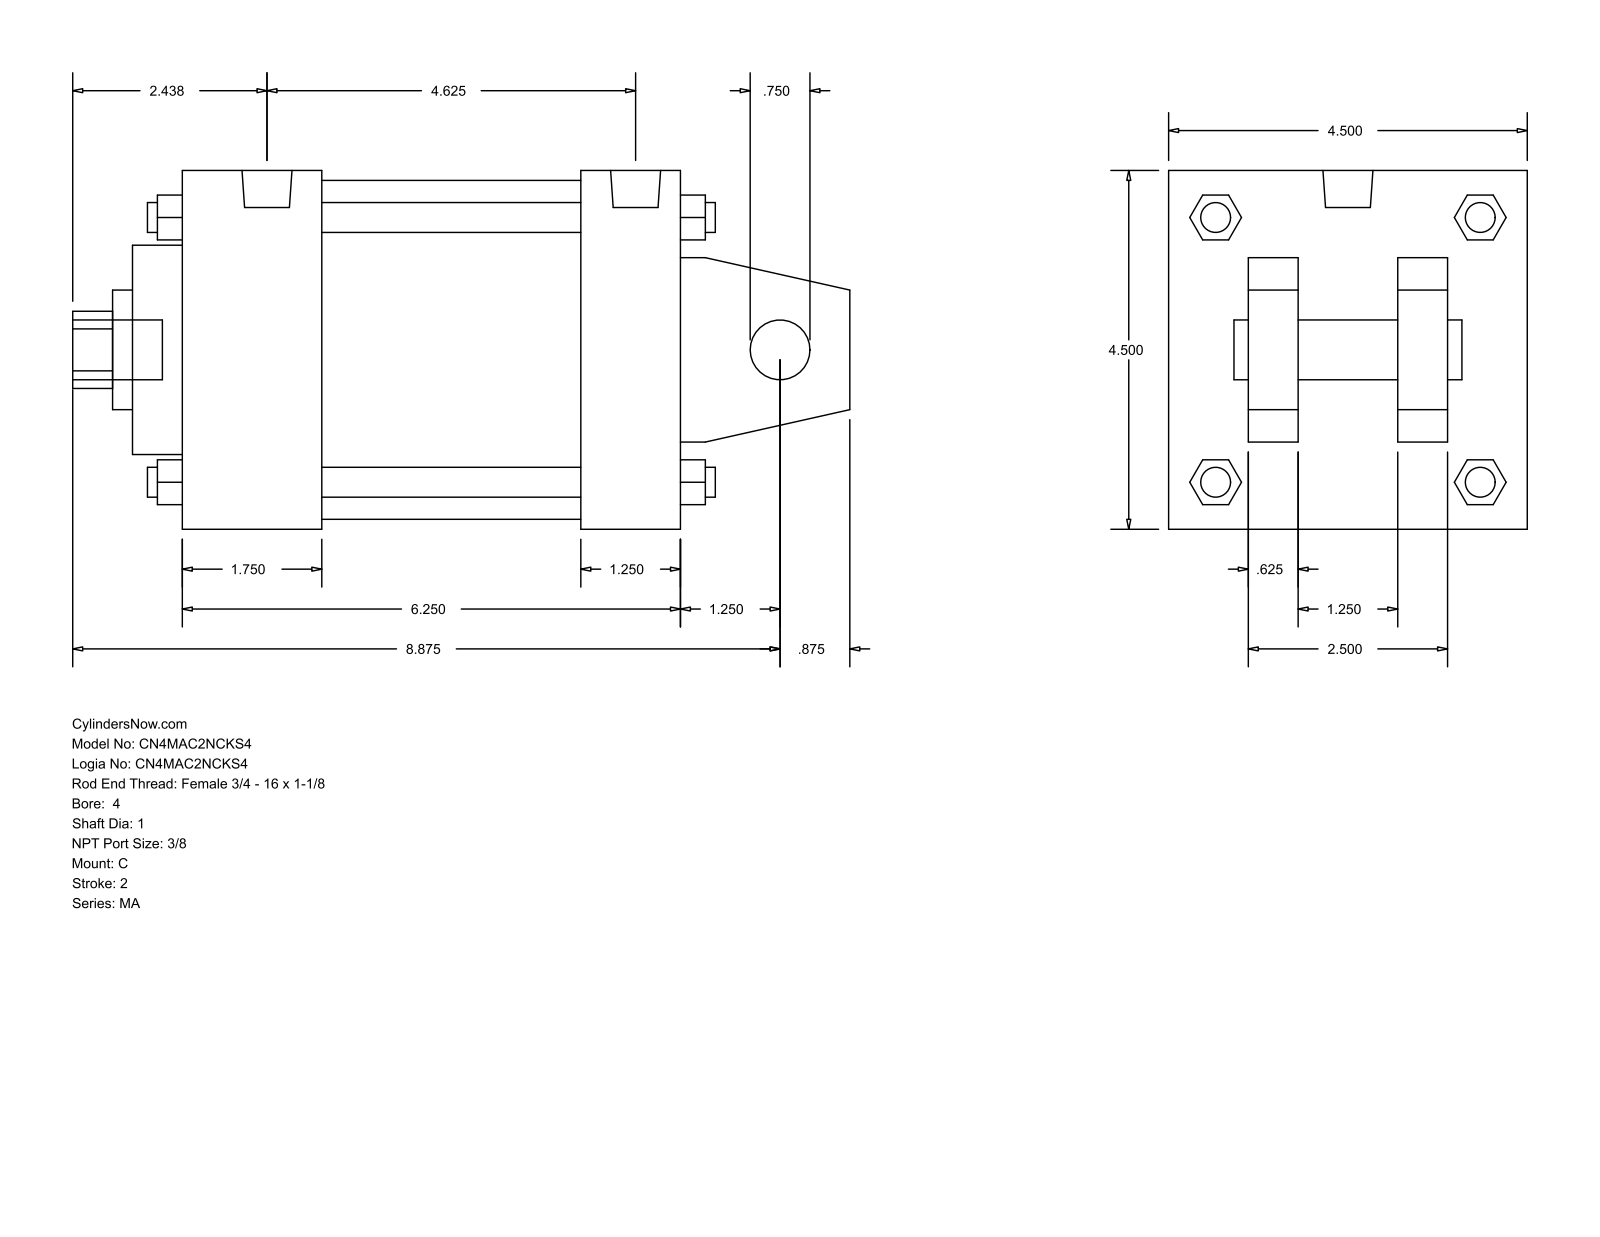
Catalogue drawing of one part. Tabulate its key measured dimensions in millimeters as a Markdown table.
| quantity | value |
| --- | --- |
| part name | MA_C__0400_1 |
| STEP written by | GSSL Pune (CONFIG_CONTROL_DESIGN) |
| units | millimeters |
| bodies | 0 solids, 141 faces (109 planar, 32 cylindrical, 0 other) |
| overall size | 247.65 × 114.3 × 114.3 |
| round holes (diameter × count) | 19.05 × 1, 25.4 × 1, 38.1 × 1, 66.67 × 1, 107.95 × 1 |
| round bosses / shafts (diameter × count) | 11.11 × 4, 9.53 × 4, 15.93 × 2, 19.05 × 1 |
| partial cylindrical surfaces (radius × count) | 12.29 × 1 |
| main face-to-face distances | 114.3, 158.76, 15.87, 73.03, 41.27, 25.4, 88.9, 47.63, 127.01, 31.75 |
